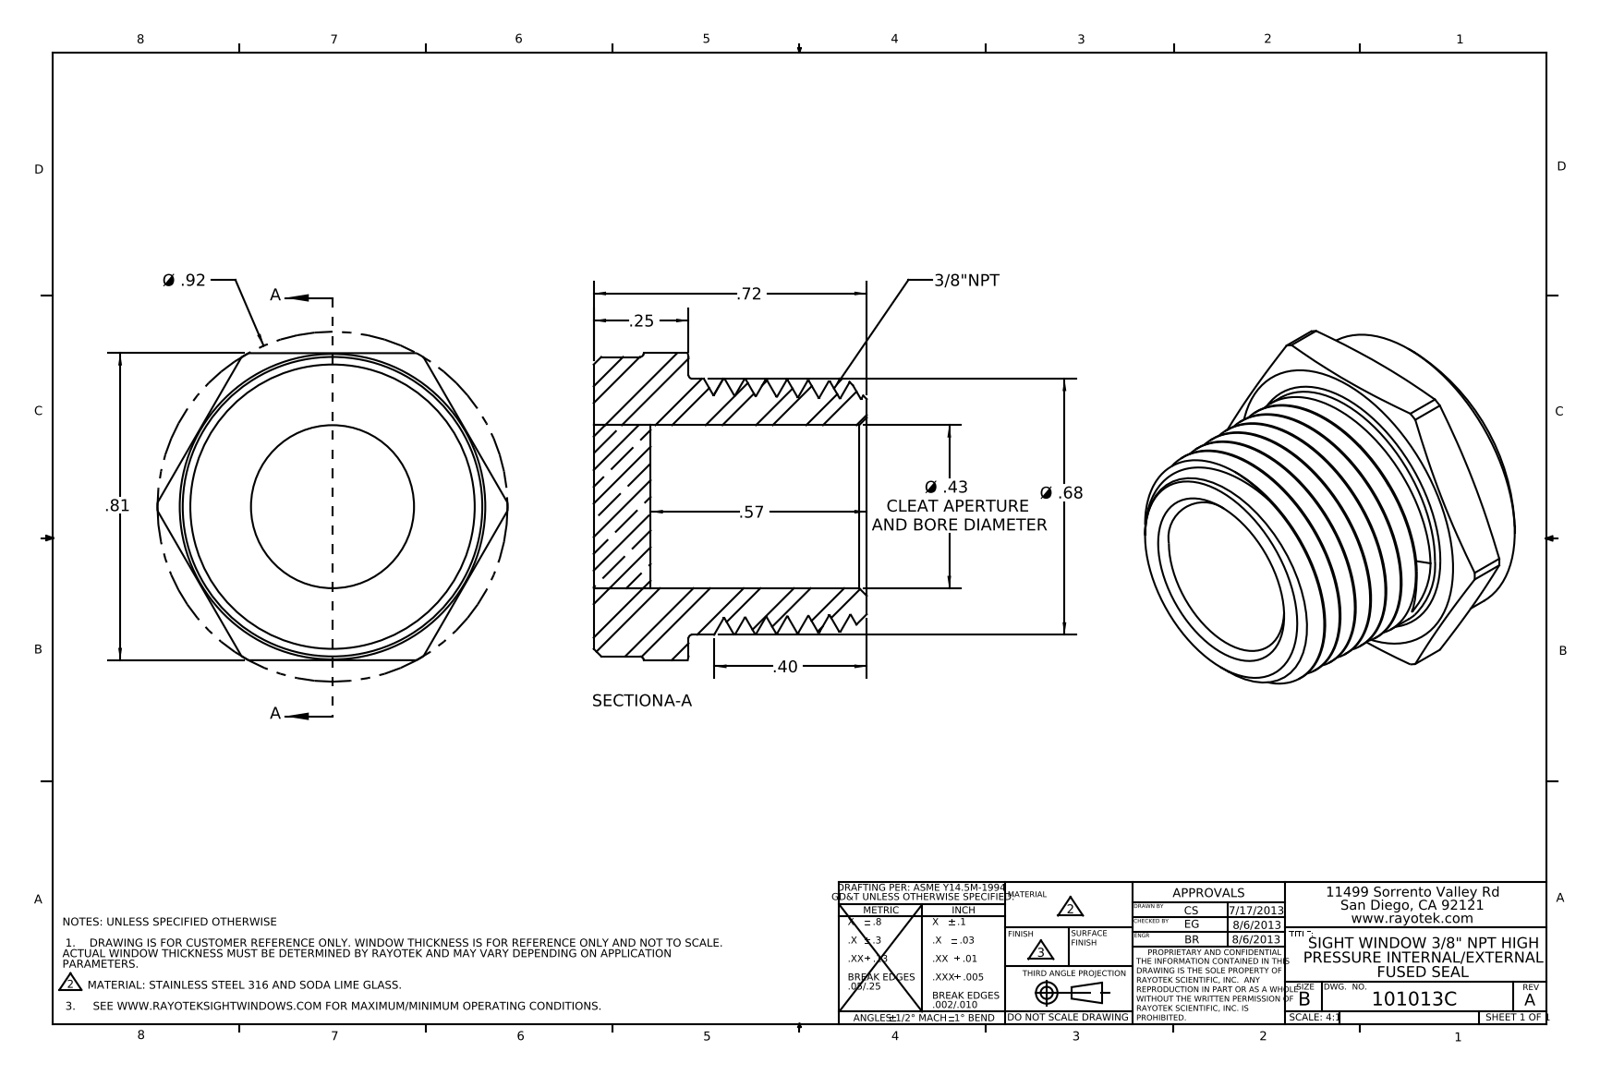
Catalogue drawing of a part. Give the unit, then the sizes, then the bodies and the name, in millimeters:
Units: millimetres
Overall size (bounding box): 23.4 × 20.6 × 18.3
Round holes (diameter × count): ⌀10.9 ×1
Round bosses / shafts (diameter × count): ⌀20.1 ×1, ⌀17.1 ×1
Partial cylindrical surfaces — rounded edges, fillets, slot ends (radius × count): R11.7 ×1
Main face-to-face distances: 3.8, 6.4, 2.5, 20.6, 18.3, 14.5, 11.9, 20.6
Volume: 3 180 mm³ · Surface area: 2 848 mm²
Bodies: 2 solids, 61 faces (14 planar, 16 cylindrical, 31 other)
Part name (STEP PRODUCT): 101013; 402013; 403013_CUSTOMER
STEP written by: SolidWorks 2012 (AUTOMOTIVE_DESIGN)
